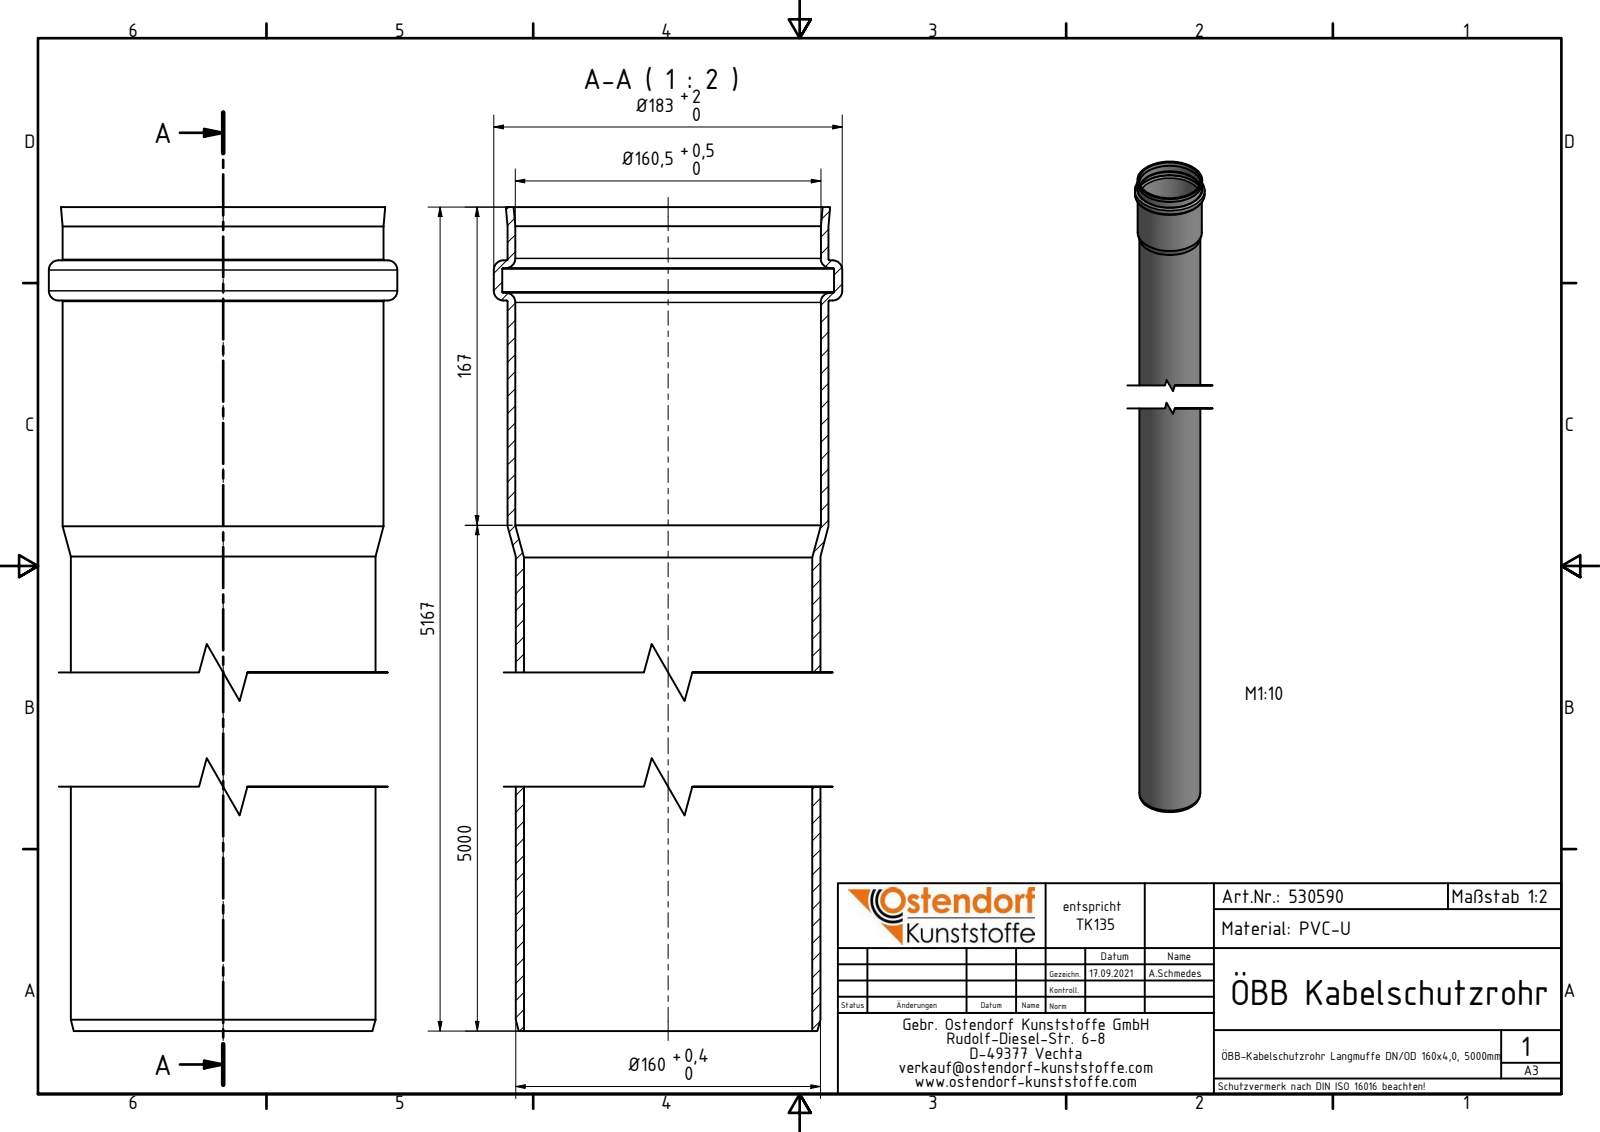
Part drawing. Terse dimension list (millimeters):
name: 530590 ÖBB-Kabelschutzrohr Langmuffe DN_OD 160x4,0, 5000mm
written by: Autodesk Inventor 2020 (AUTOMOTIVE_DESIGN)
unit: mm
bodies: 1 solid, 27 faces (6 planar, 8 cylindrical, 13 other)
size: 5167 × 183 × 183
volume: 10 880 000 mm³; area: 5 080 000 mm²
holes: 1× ⌀151.4, 1× ⌀160.5, 1× ⌀174.3
bosses: 1× ⌀183, 1× ⌀168.5, 1× ⌀160
face distances: 4, 17, 5167, 5139, 28, 5118, 21, 49, 5135, 32
